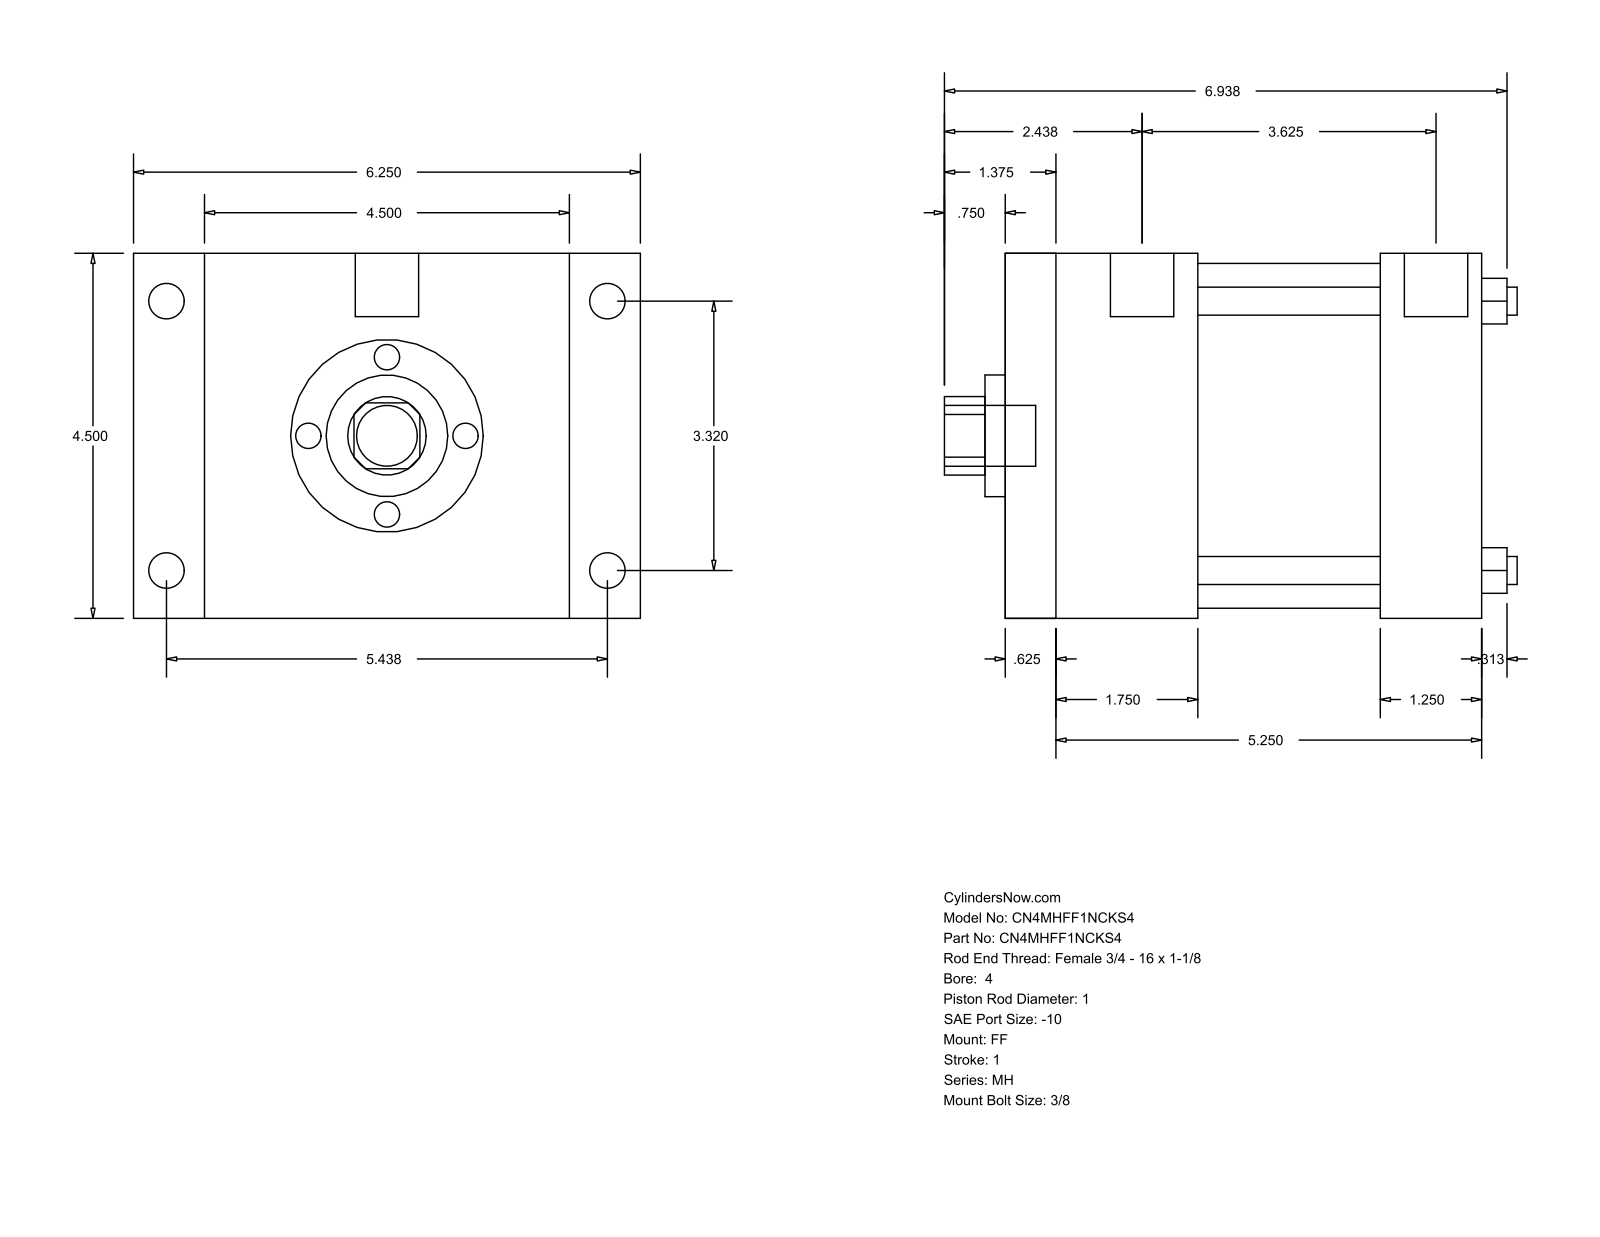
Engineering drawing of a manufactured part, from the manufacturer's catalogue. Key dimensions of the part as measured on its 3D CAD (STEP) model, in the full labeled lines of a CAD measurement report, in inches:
Part name (STEP PRODUCT): MH_FF__0400_1
STEP written by: GSSL Pune (CONFIG_CONTROL_DESIGN)
Units: inches
Bodies: 0 solids, 92 faces (64 planar, 28 cylindrical, 0 other)
Overall size (bounding box): 7.063 × 6.25 × 4.5
Round holes (diameter × count): ⌀0.345 ×4, ⌀1 ×1, ⌀1.5 ×1, ⌀4.25 ×1
Round bosses / shafts (diameter × count): ⌀0.438 ×4, ⌀0.344 ×4, ⌀0.781 ×2, ⌀0.75 ×1
Partial cylindrical surfaces — rounded edges, fillets, slot ends (radius × count): R0.484 ×1
Main face-to-face distances: 4.5, 5.875, 0.625, 5.25, 5.375, 2.375, 1.75, 3.5, 4.625, 4
Hole centre spacings: 2.347, 3.32, 4.695
